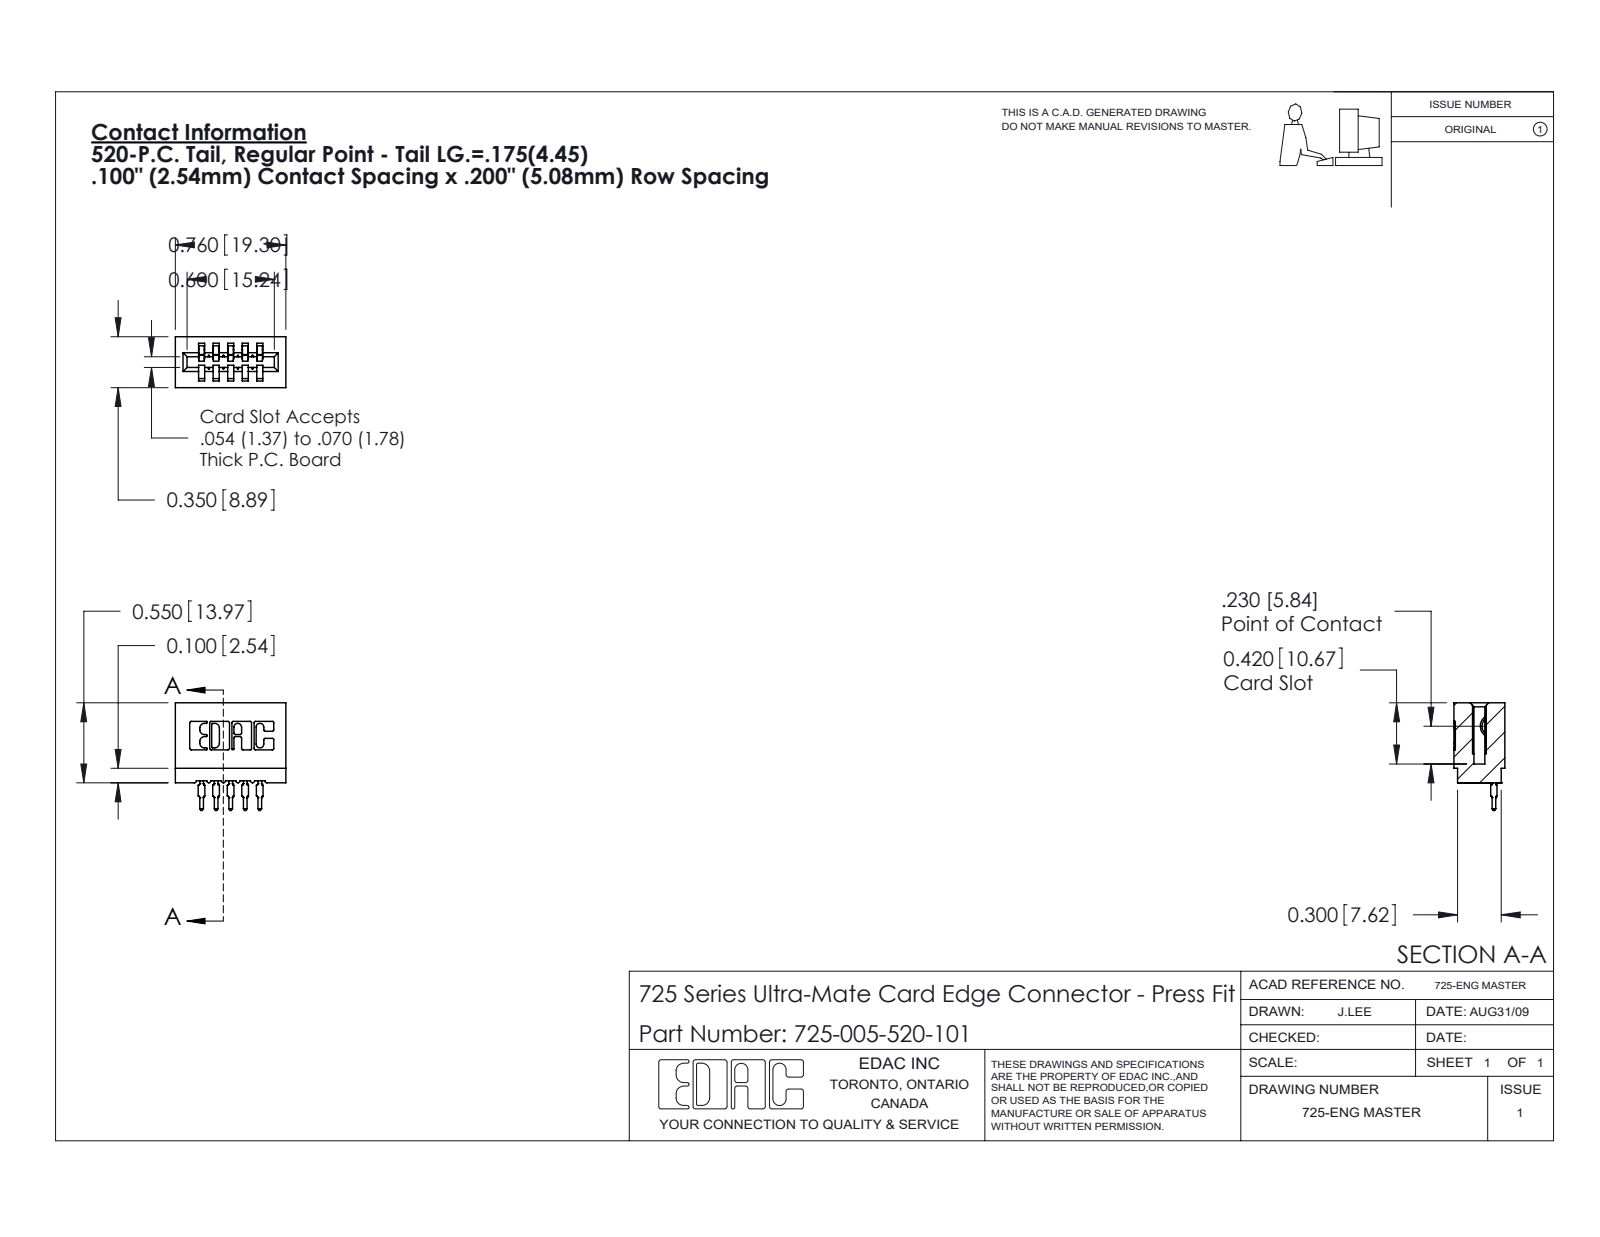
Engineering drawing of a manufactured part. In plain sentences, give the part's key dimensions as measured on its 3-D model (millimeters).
The part is named "745-292-001_520; 725 Part_Insulator Option - 01; 725-005-520-101". Its 3-D file was written by "SolidWorks 2020 (CONFIG_CONTROL_DESIGN)". It is 6 solids with 655 faces: 390 planar, 135 cylindrical and 130 other. Overall it measures 19.3 by 18.8 by 8.9 millimeters. Its volume is 1 670 cubic millimeters and its surface area 2 505 square millimeters. Partial cylindrical surfaces (rounded edges, fillets, slot ends): 22 of radius 0.3, 10 of radius 0.4, 10 of radius 0.5, 6 of radius 0.2, 6 of radius 0.8, 4 of radius 0.1, 4 of radius 0.3, 3 of radius 0.7. The main face-to-face distances are 2.5, 5.1, 1.1, 1.5, 3.6, 7.6, 4, 6.1, 5.4, 8.9.
